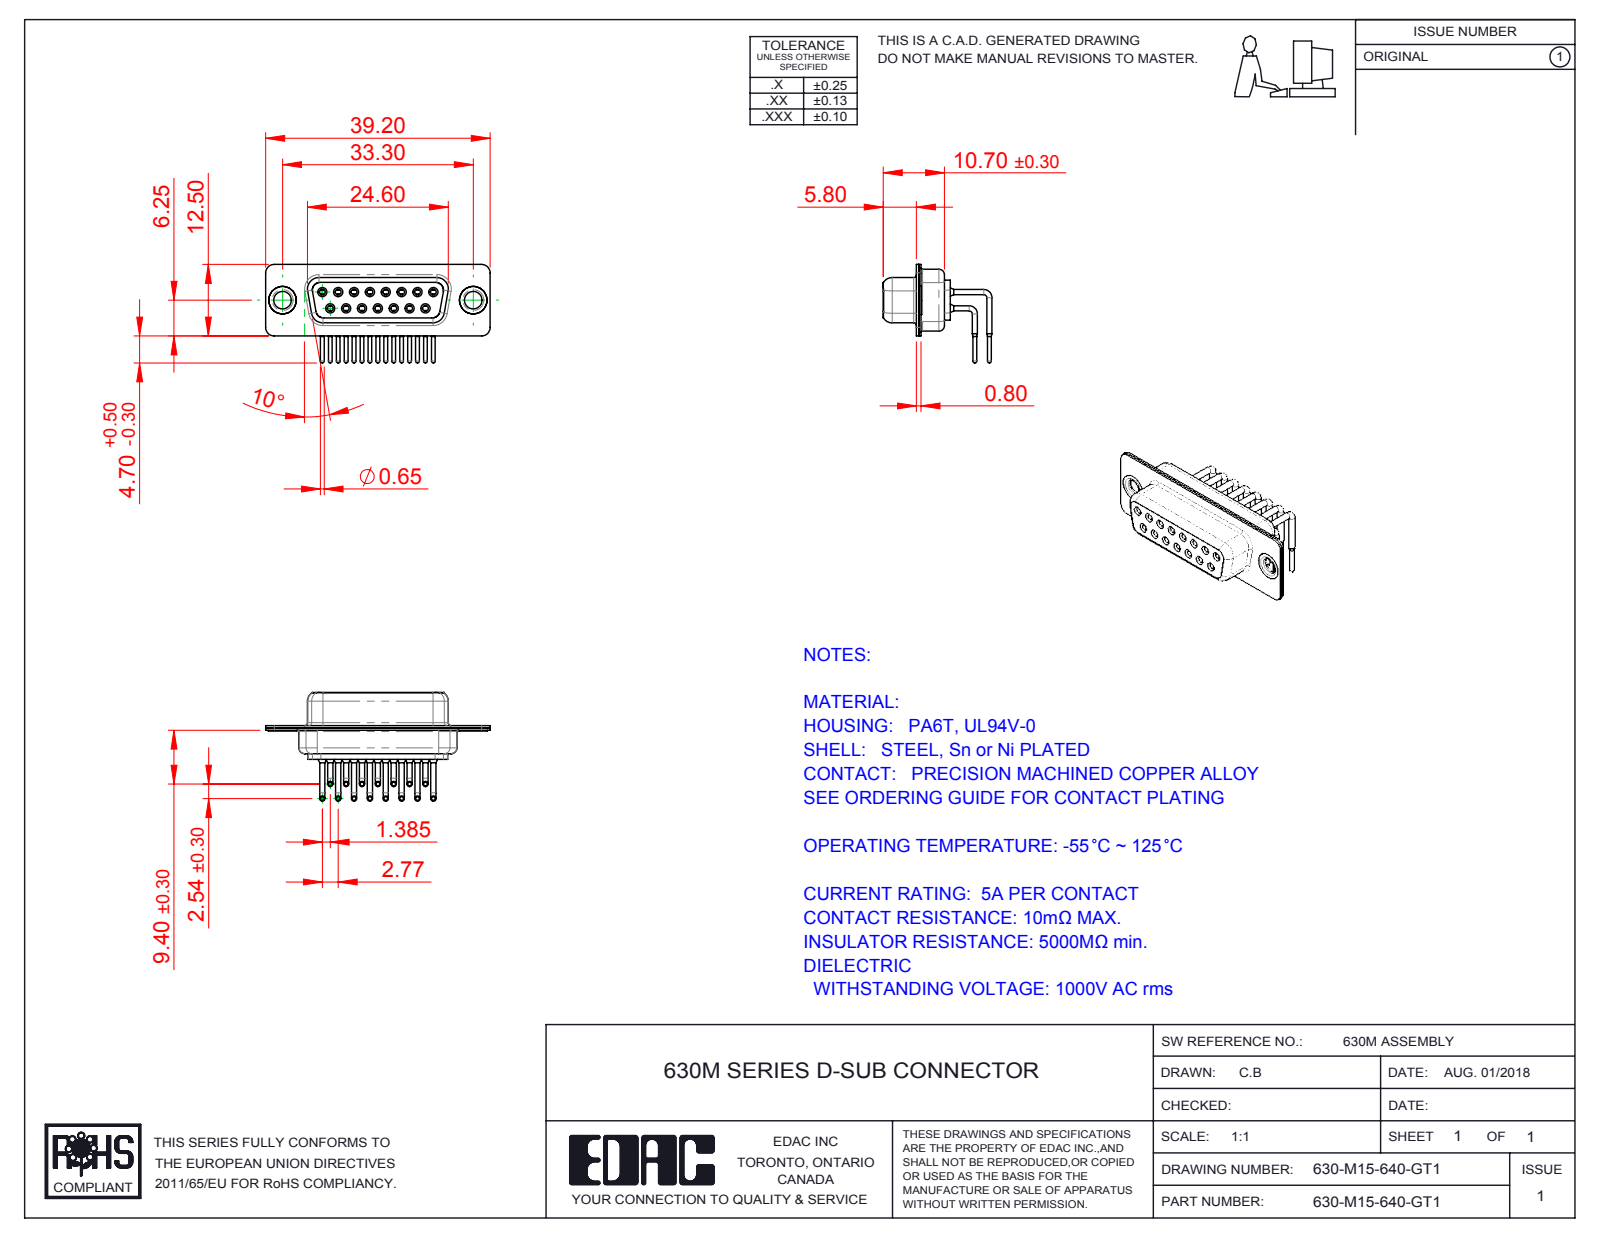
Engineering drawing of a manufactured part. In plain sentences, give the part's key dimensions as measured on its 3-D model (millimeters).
The part is named "630M Thru Hole Rivet; 630M Contact Row 1; 630M Housing_15 Contacts; 630M Shell Rear_15 Contacts (+3 more)". Its 3-D file was written by "SolidWorks 2016 (CONFIG_CONTROL_DESIGN)". It is 20 solids with 1048 faces: 292 planar, 466 cylindrical and 290 other. Overall it measures 39.2 by 18.99 by 17.2 millimeters. Its volume is 2 488 cubic millimeters and its surface area 6 404 square millimeters. Round holes: 15 of diameter 1, 15 of diameter 1.1, 15 of diameter 1.7, 15 of diameter 1.8, 15 of diameter 2, 2 of diameter 3.05, 2 of diameter 4, 2 of diameter 4.8. Round bosses or shafts: 30 of diameter 0.9, 15 of diameter 1.6, 15 of diameter 1.5, 15 of diameter 0.65, 2 of diameter 5, 2 of diameter 4.9, 2 of diameter 3.55. Partial cylindrical surfaces (rounded edges, fillets, slot ends): 16 of radius 1.5, 12 of radius 2, 8 of radius 1.35, 8 of radius 1.6, 4 of radius 0.25, 4 of radius 0.5, 4 of radius 0.6, 4 of radius 0.65. The main face-to-face distances are 0.4, 1.45, 8.95, 6.2, 1.9, 8.5, 2.3, 0.45, 7.05, 0.85. The hole center spacings are 3.16, 2.77, 5.54, 8.31, 11.08, 5.03, 5.04, 7.48.
